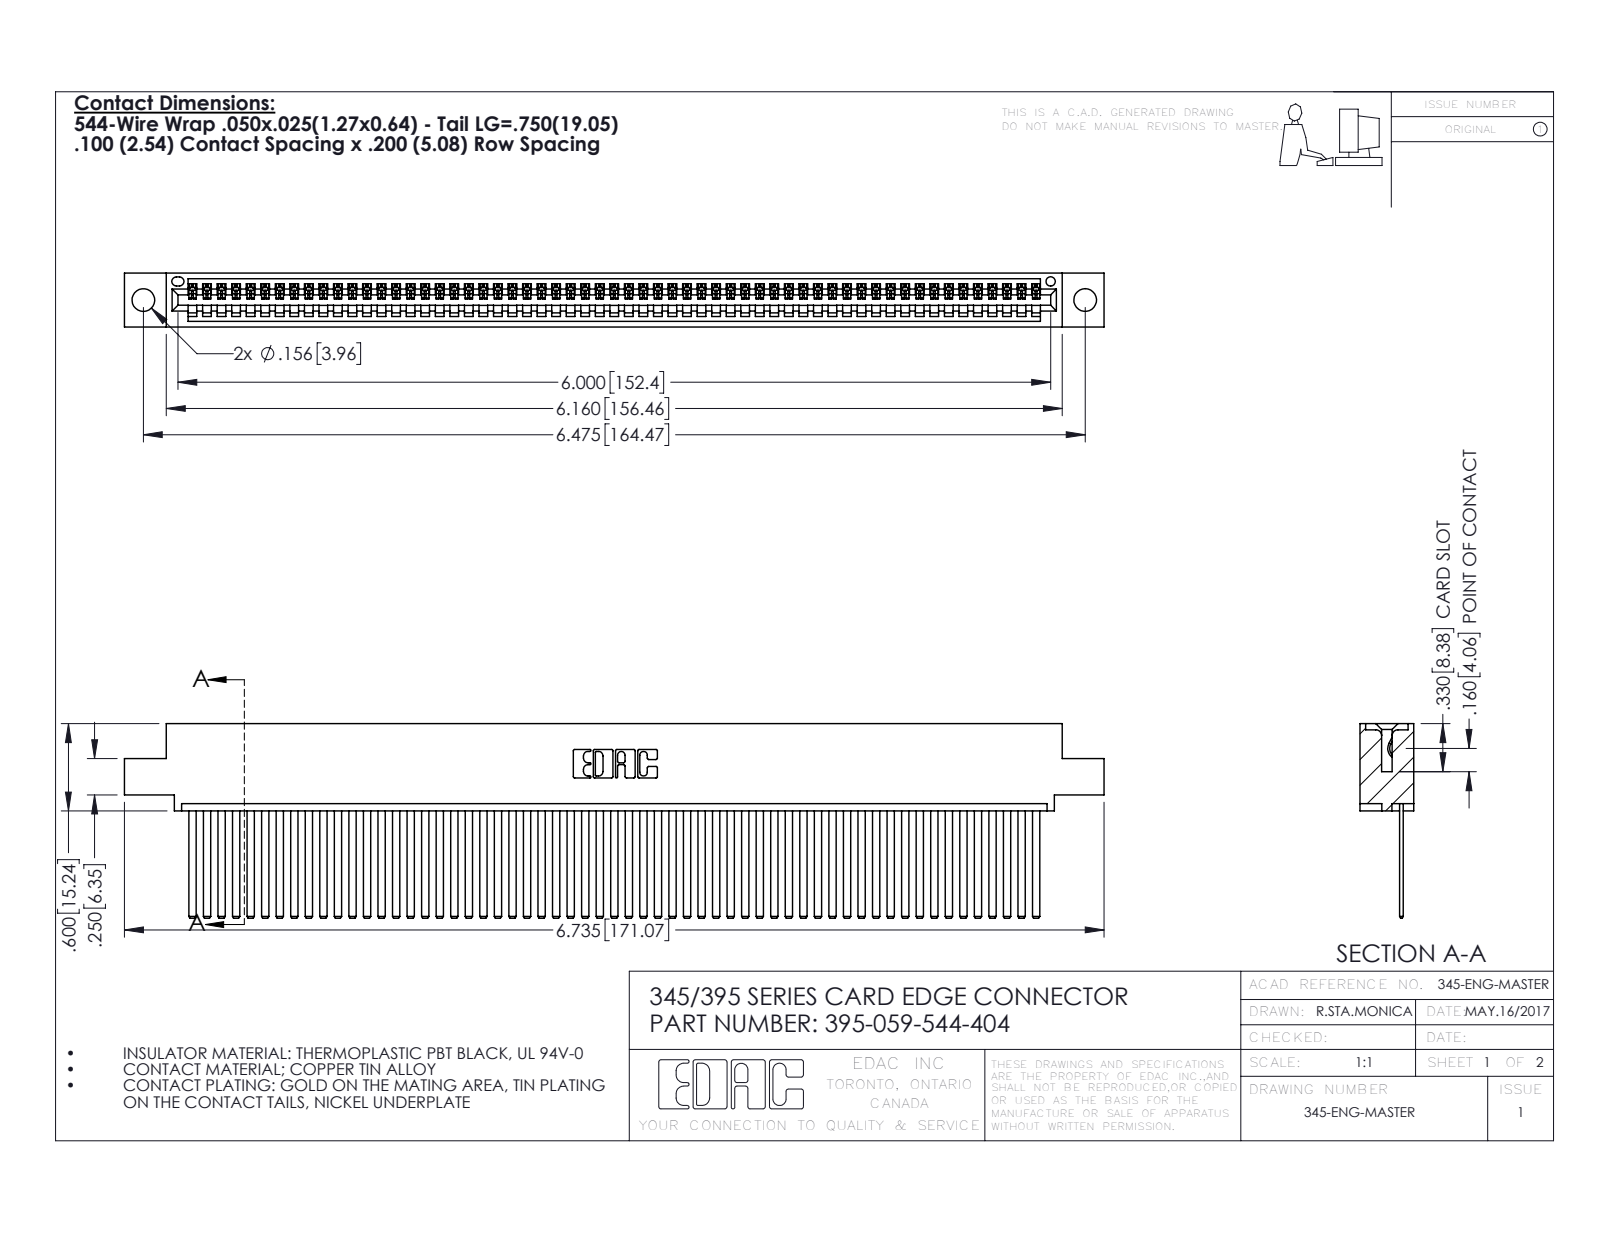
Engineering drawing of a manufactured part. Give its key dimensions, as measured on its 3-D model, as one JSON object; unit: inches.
{"part_name": "345 Part_0.110 Offset - 0.156 Dia-TH; 395-059-544-404; 345-292-001_345-293-144", "step_written_by": "SolidWorks 2016 (CONFIG_CONTROL_DESIGN)", "units": "inches", "bodies": {"solids": 60, "faces": 3198, "planar": 2208, "cylindrical": 990, "other": 0}, "overall_size": [6.735, 1.337, 0.37], "volume_in3": 1.032, "surface_area_in2": 38.2, "round_holes": [[0.156, 2], [0.064, 1]], "partial_cylinders_radius": [[0.006, 118], [0.01, 22], [0.007, 6], [0.031, 6], [0.026, 3], [0.031, 2], [0.04, 2], [0.014, 1]], "face_to_face_distances": [0.072, 0.298, 0.025, 0.098, 0.272, 0.37, 0.2, 0.225, 0.149, 0.072], "hole_center_spacings": [0.27, 6.239, 6.475]}
